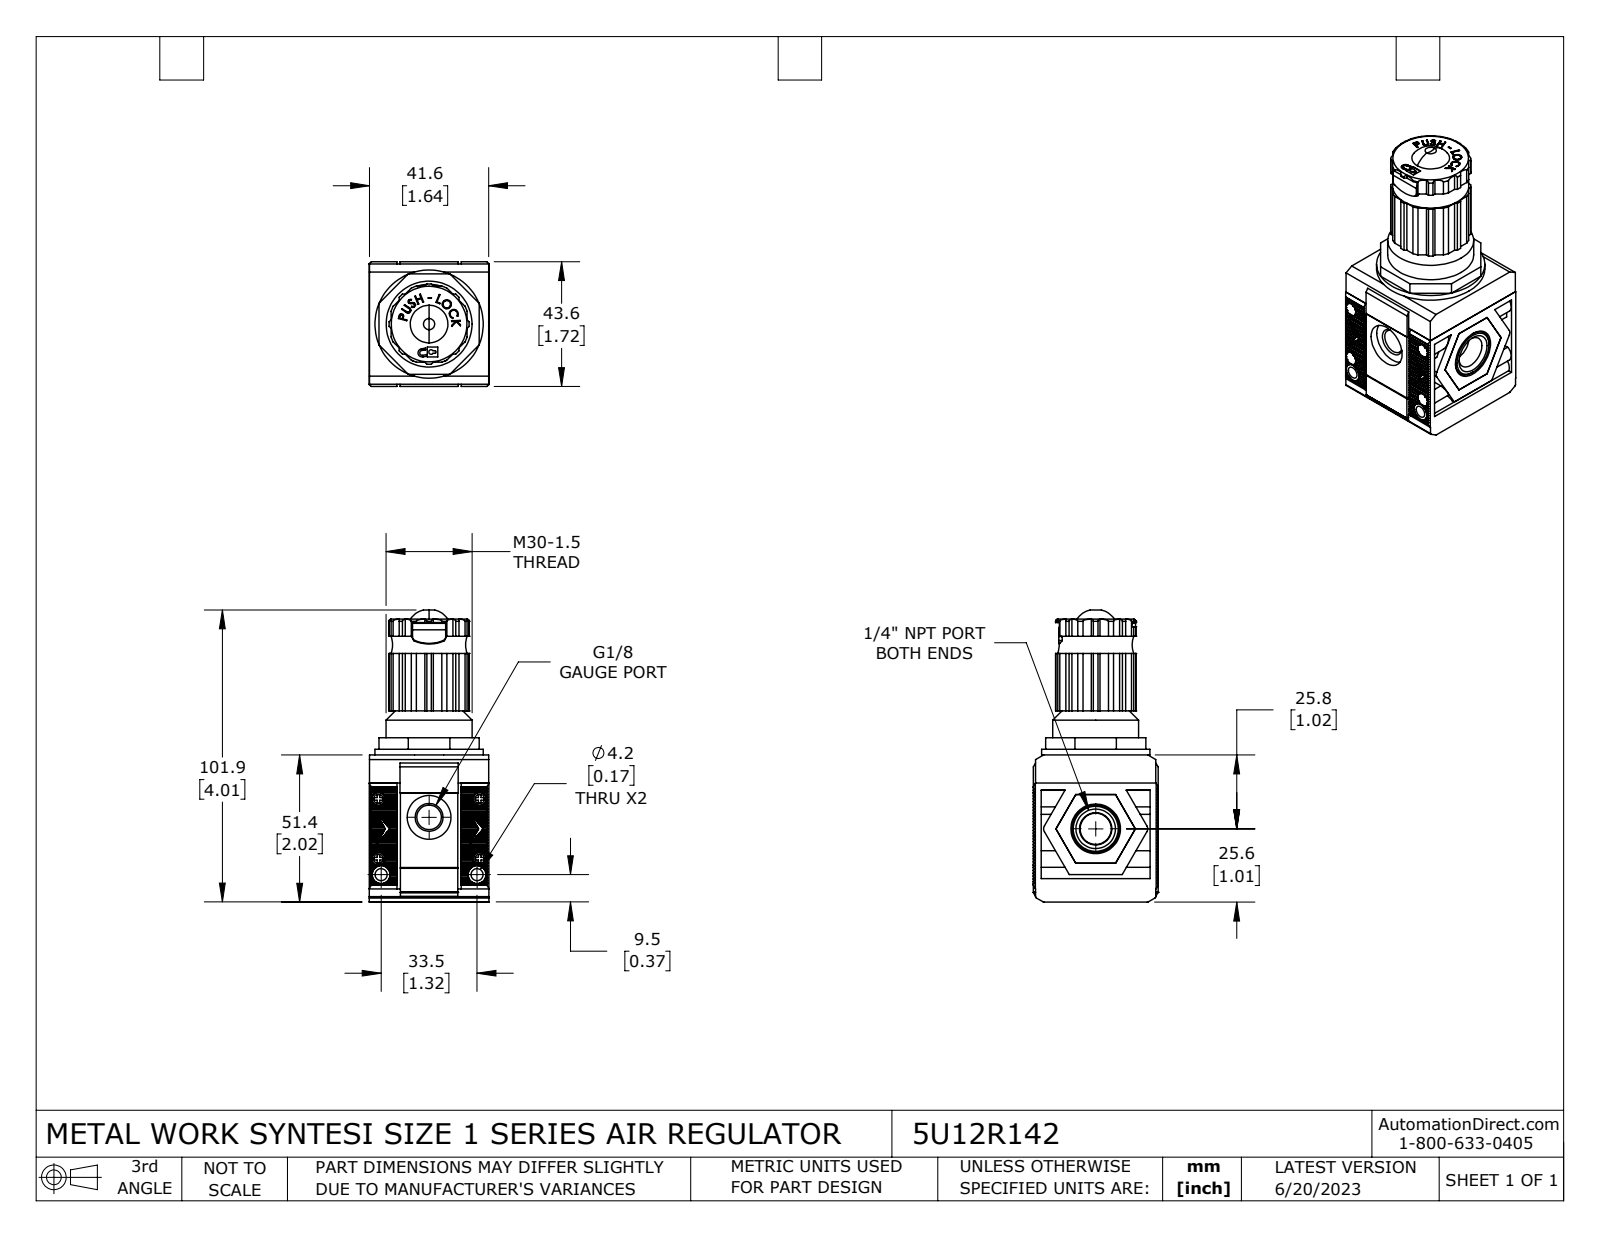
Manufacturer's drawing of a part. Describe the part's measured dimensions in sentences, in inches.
The part is named "5U12R142". Its 3-D file was written by "SolidWorks 2021 (CONFIG_CONTROL_DESIGN)". It is 13 solids with 1382 faces: 967 planar, 300 cylindrical and 115 other. Overall it measures 4.016 by 1.717 by 1.646 inches. Its volume is 7.623 cubic inches and its surface area 60.46 square inches. Round holes: 4 of diameter 0.083, 4 of diameter 0.118, 4 of diameter 0.185, 2 of diameter 0.138, 2 of diameter 0.165, 1 of diameter 0.094, 1 of diameter 0.252, 1 of diameter 0.337, 1 of diameter 0.602, 1 of diameter 1.117. Round bosses or shafts: 4 of diameter 0.181, 4 of diameter 0.102, 2 of diameter 0.244, 1 of diameter 1.488, 1 of diameter 1.26, 1 of diameter 1.181, 1 of diameter 0.898, 1 of diameter 0.717. Partial cylindrical surfaces (rounded edges, fillets, slot ends): 4 of radius 0.024, 4 of radius 0.122, 3 of radius 0.059, 2 of radius 0.008, 2 of radius 0.051, 2 of radius 0.079, 1 of radius 0.016, 1 of radius 0.018. The main face-to-face distances are 0.386, 1.638, 2.024, 1.642, 0.067, 1.646, 1.673, 1.575, 0.043, 0.307. The hole center spacings are 0.222, 0.362, 0.742, 0.785, 0.823, 0.9, 1.027, 1.042.
